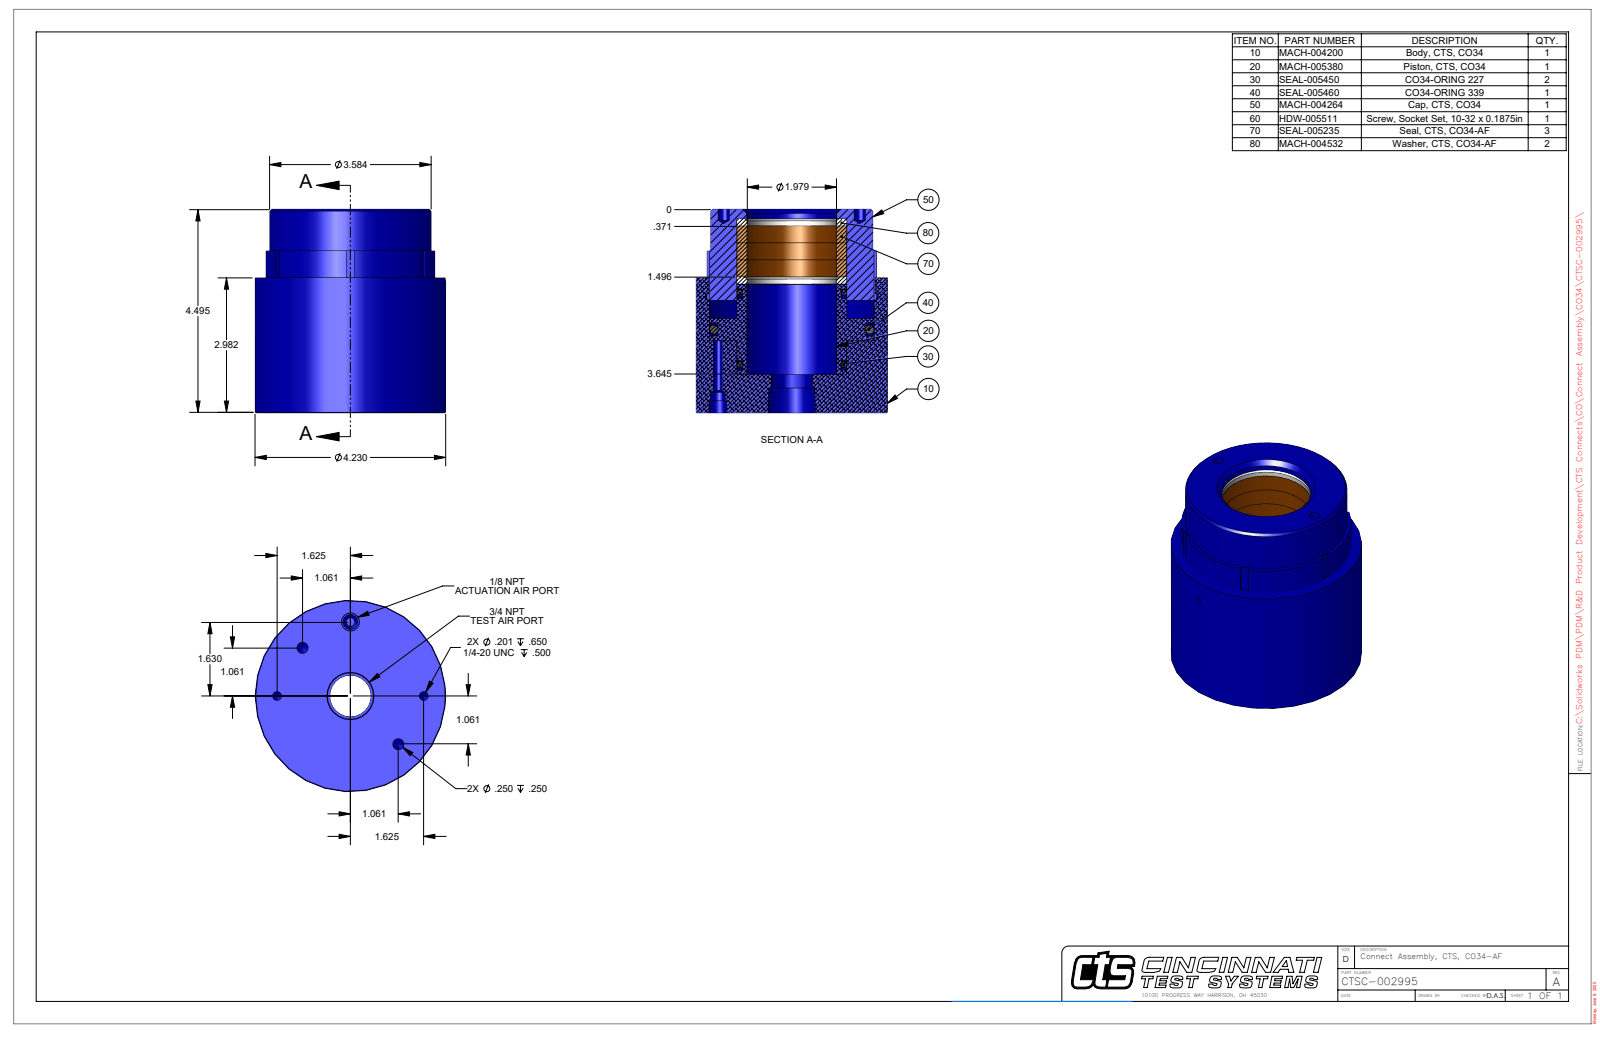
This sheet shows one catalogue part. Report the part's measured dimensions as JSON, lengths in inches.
{"part_name": "CTSC-002995", "step_written_by": "SolidWorks 2023 (AUTOMOTIVE_DESIGN)", "units": "inches", "bodies": {"solids": 1, "faces": 132, "planar": 48, "cylindrical": 58, "other": 26}, "overall_size": [4.495, 4.231, 4.23], "volume_in3": 45.55, "surface_area_in2": 114.4, "round_holes": [[0.25, 4], [0.201, 2], [0.125, 1], [0.159, 1], [0.187, 1], [0.332, 1], [0.906, 1], [1.979, 1], [1.981, 1], [1.987, 1], [1.988, 1], [2.102, 1]], "round_bosses_or_shafts": [[4.23, 1], [3.75, 1], [3.584, 1], [2.416, 1]], "partial_cylinders_radius": [[1.844, 1], [2.097, 1]], "face_to_face_distances": [4.495, 2.982, 1.513, 0.85, 2.132, 3.645, 3.575, 2.725, 0.593, 0.92], "hole_center_spacings": [1.5, 2.211, 1.148, 1.201, 1.625, 2.302, 2.772, 2.887]}
